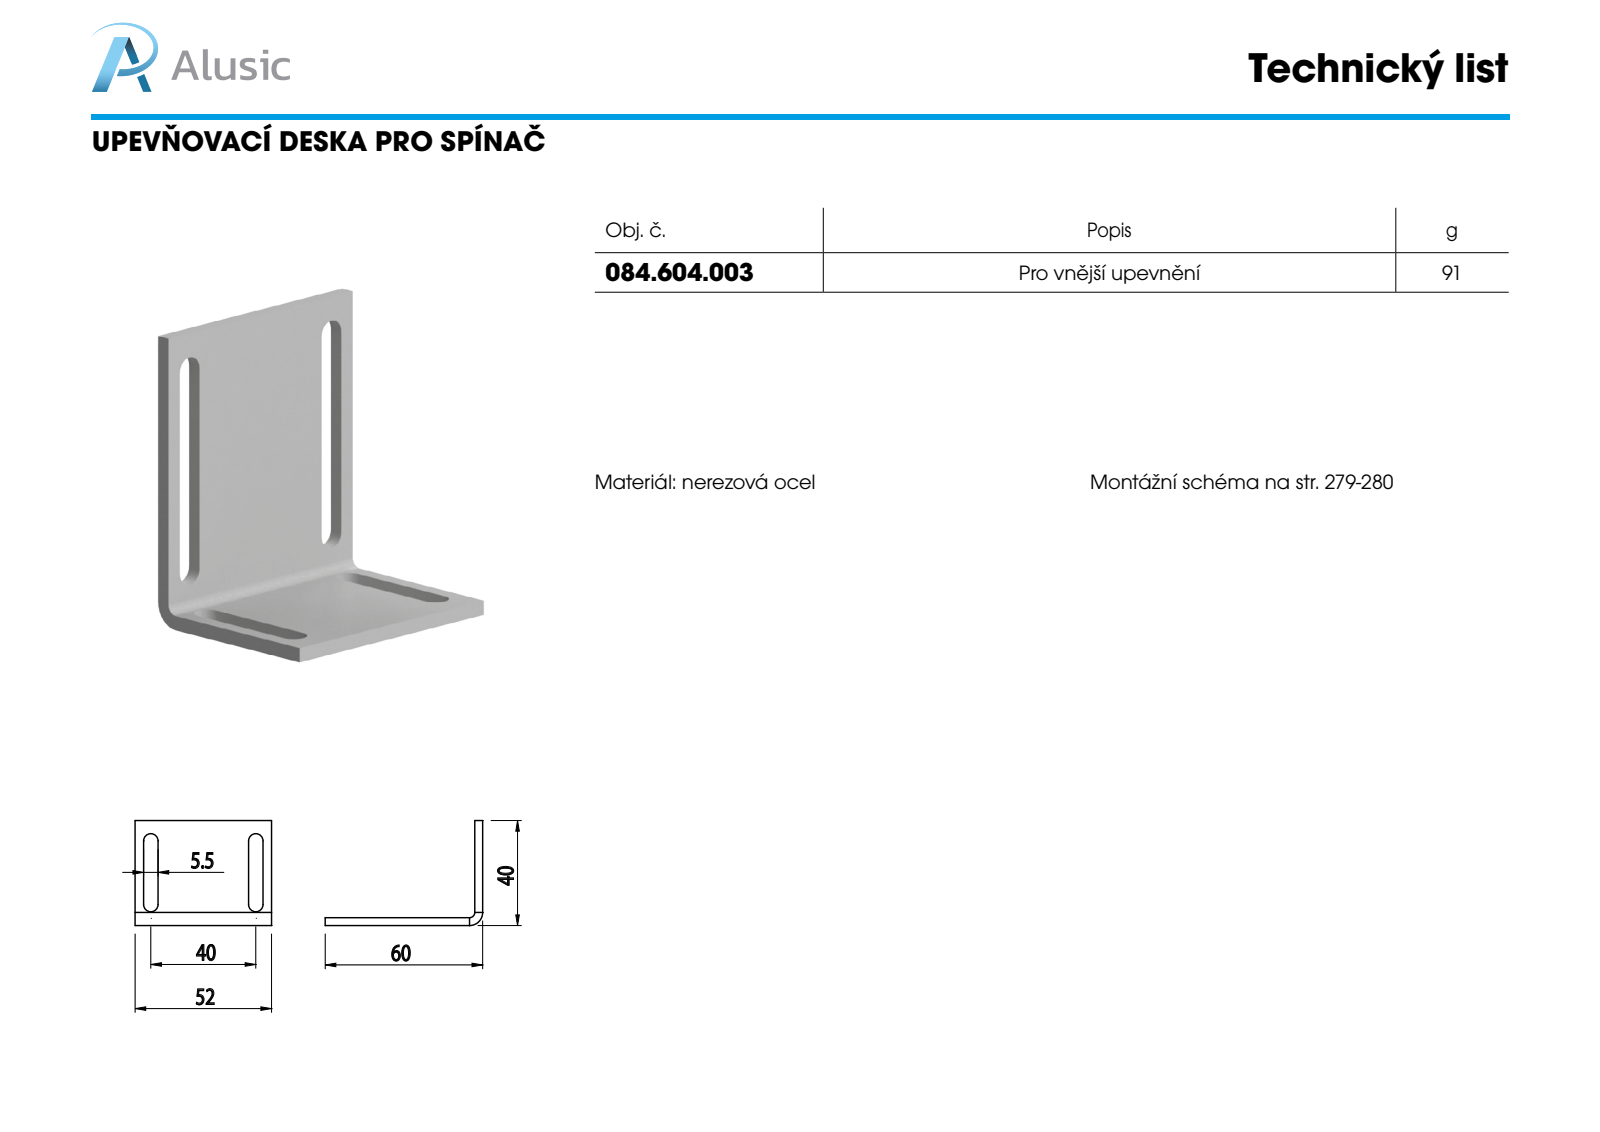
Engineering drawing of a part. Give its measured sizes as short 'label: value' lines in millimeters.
name: 084.604.003
written by: SolidWorks 2012 (CONFIG_CONTROL_DESIGN)
unit: mm
bodies: 1 solid, 32 faces (20 planar, 12 cylindrical, 0 other)
size: 60 × 52 × 40
volume: 12 443 mm³; area: 10 177 mm²
rounds: 8× R2.75, 1× R2, 1× R5
face distances: 3, 40, 3.25, 48.75, 8.75, 43.25, 5.5, 52, 45.5, 34.5
